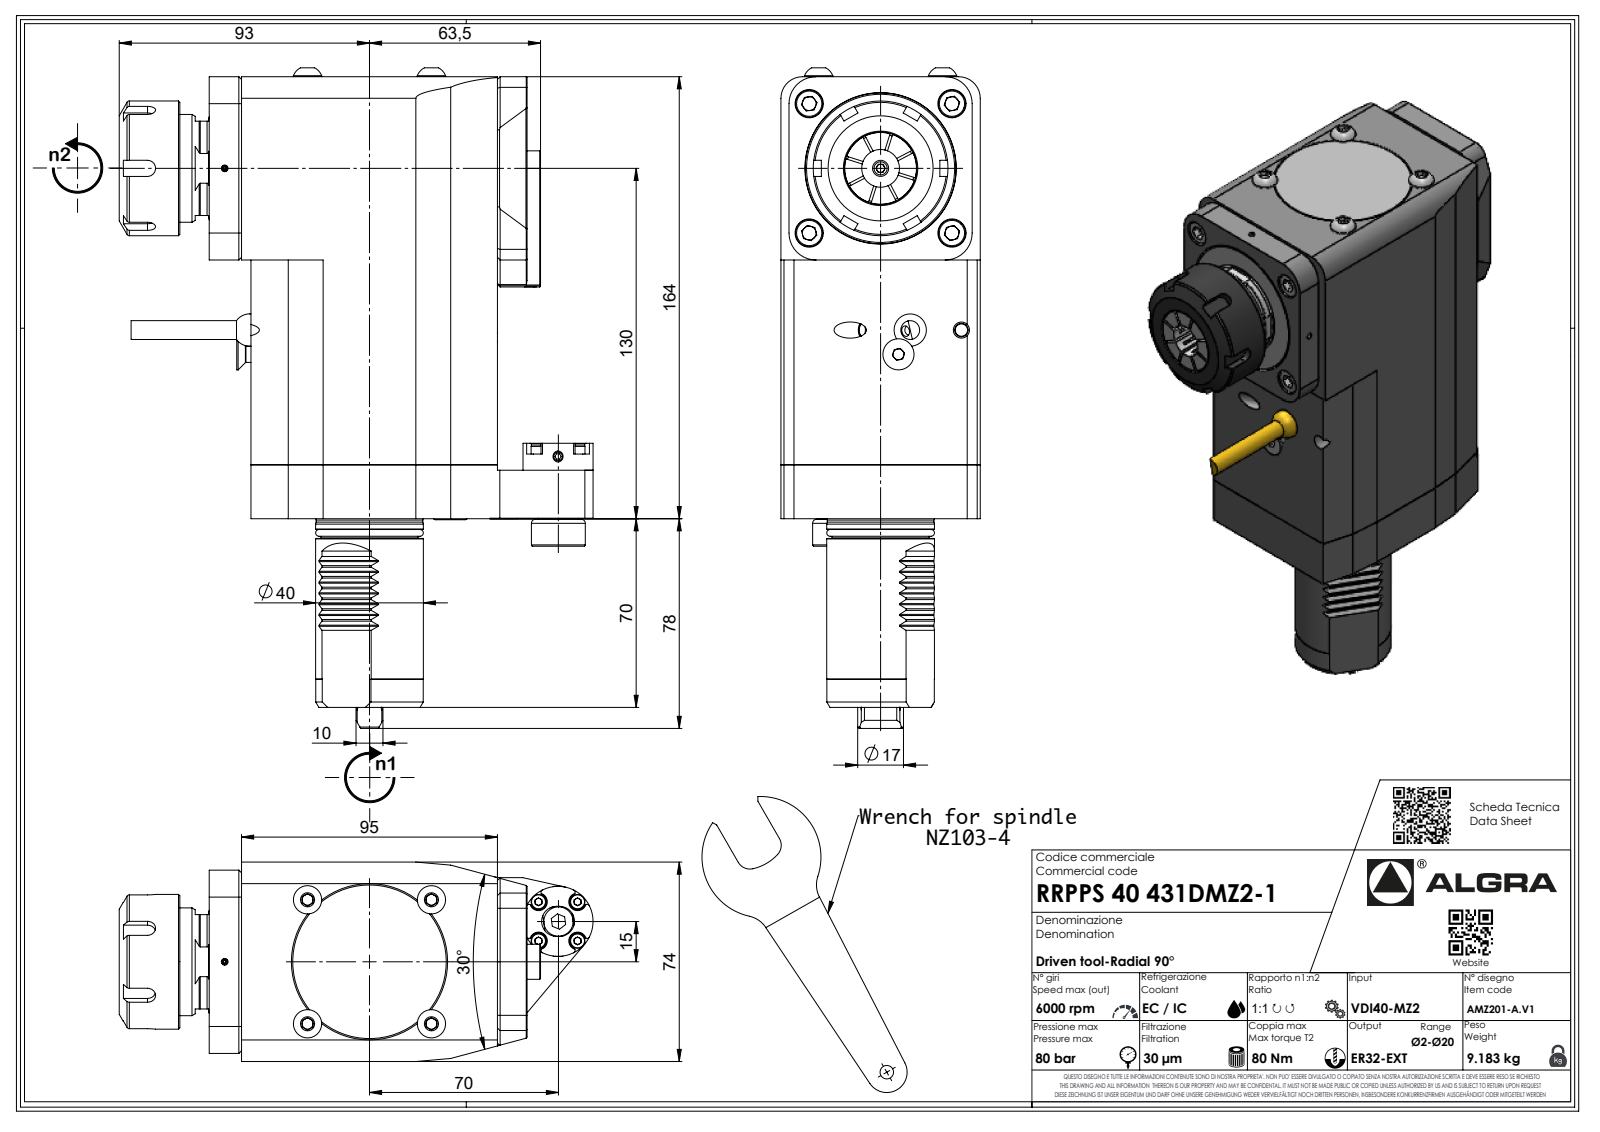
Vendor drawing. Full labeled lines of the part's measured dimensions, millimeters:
Part name (STEP PRODUCT): RRPPS40431DMZ2-1
STEP written by: SolidWorks 2023 (AUTOMOTIVE_DESIGN)
Units: millimetres
Bodies: 3 solids, 664 faces (406 planar, 109 cylindrical, 149 other)
Overall size (bounding box): 245.1 × 175.91 × 74
Volume: 1 373 000 mm³ · Surface area: 105 439 mm²
Round holes (diameter × count): ⌀2.1 ×1, ⌀4 ×1, ⌀44.2 ×1, ⌀48.2 ×1, ⌀52.2 ×1, ⌀56.2 ×1
Round bosses / shafts (diameter × count): ⌀10.5 ×4, ⌀40 ×2, ⌀56 ×1, ⌀52 ×1, ⌀50 ×1, ⌀48 ×1, ⌀44 ×1, ⌀39.9 ×1
Partial cylindrical surfaces — rounded edges, fillets, slot ends (radius × count): R1 ×8, R0.3 ×7, R0.33 ×7, R0.52 ×7, R3 ×7, R3.7 ×7, R10 ×6, R6 ×4
Main face-to-face distances: 74, 164, 91.5, 15.5, 11, 107, 118, 102.5, 76.7, 84.92
